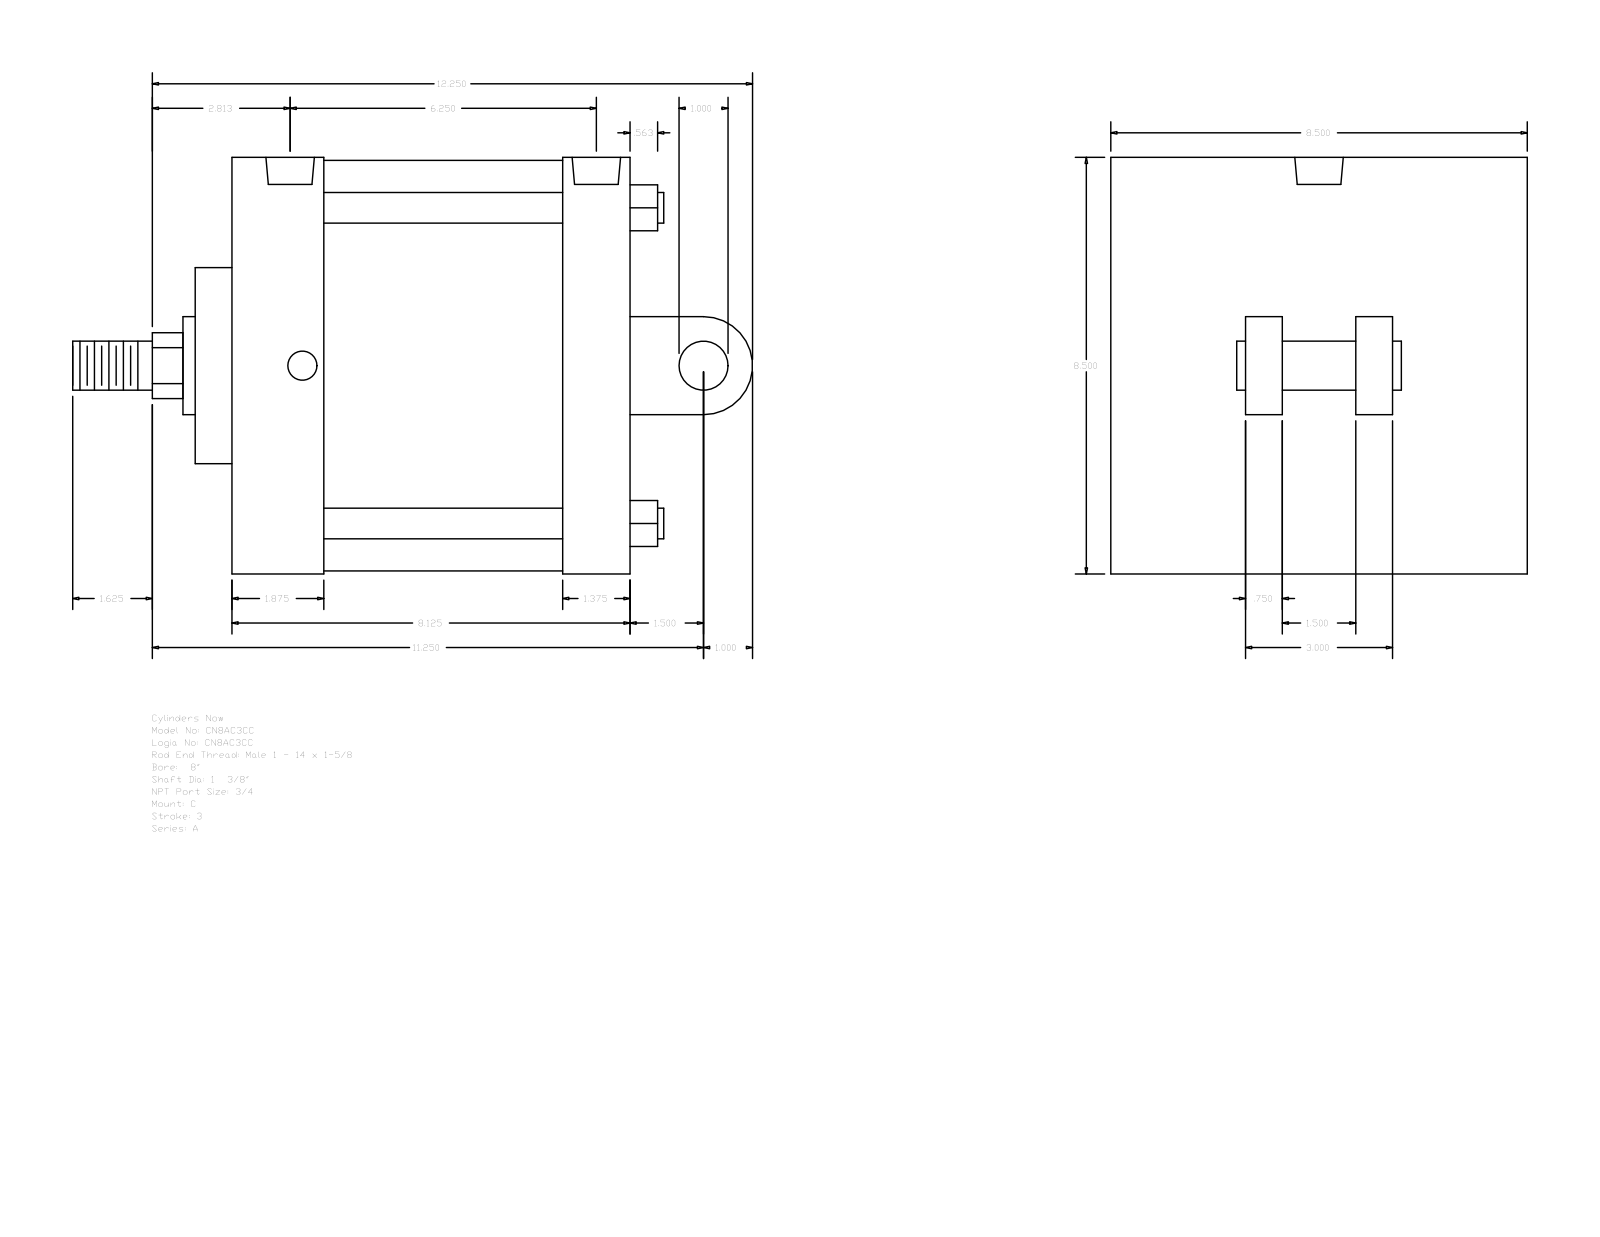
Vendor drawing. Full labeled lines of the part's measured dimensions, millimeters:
Part name (STEP PRODUCT): A_C__0800_1.375
STEP written by: GSSL Pune (CONFIG_CONTROL_DESIGN)
Units: millimetres
Bodies: 0 solids, 104 faces (75 planar, 29 cylindrical, 0 other)
Overall size (bounding box): 352.43 × 215.9 × 215.9
Round holes (diameter × count): ⌀15.08 ×4, ⌀25.12 ×2
Round bosses / shafts (diameter × count): ⌀15.88 ×4, ⌀25.4 ×2, ⌀212.72 ×1, ⌀50.8 ×1, ⌀34.92 ×1
Partial cylindrical surfaces — rounded edges, fillets, slot ends (radius × count): R17.06 ×1, R25.4 ×1
Main face-to-face distances: 206.38, 215.9, 158.75, 57.15, 47.63, 171.45, 123.82, 34.93, 88.9, 69.85
Hole centre spacings: 6.35, 146.05, 152.4, 158.75
